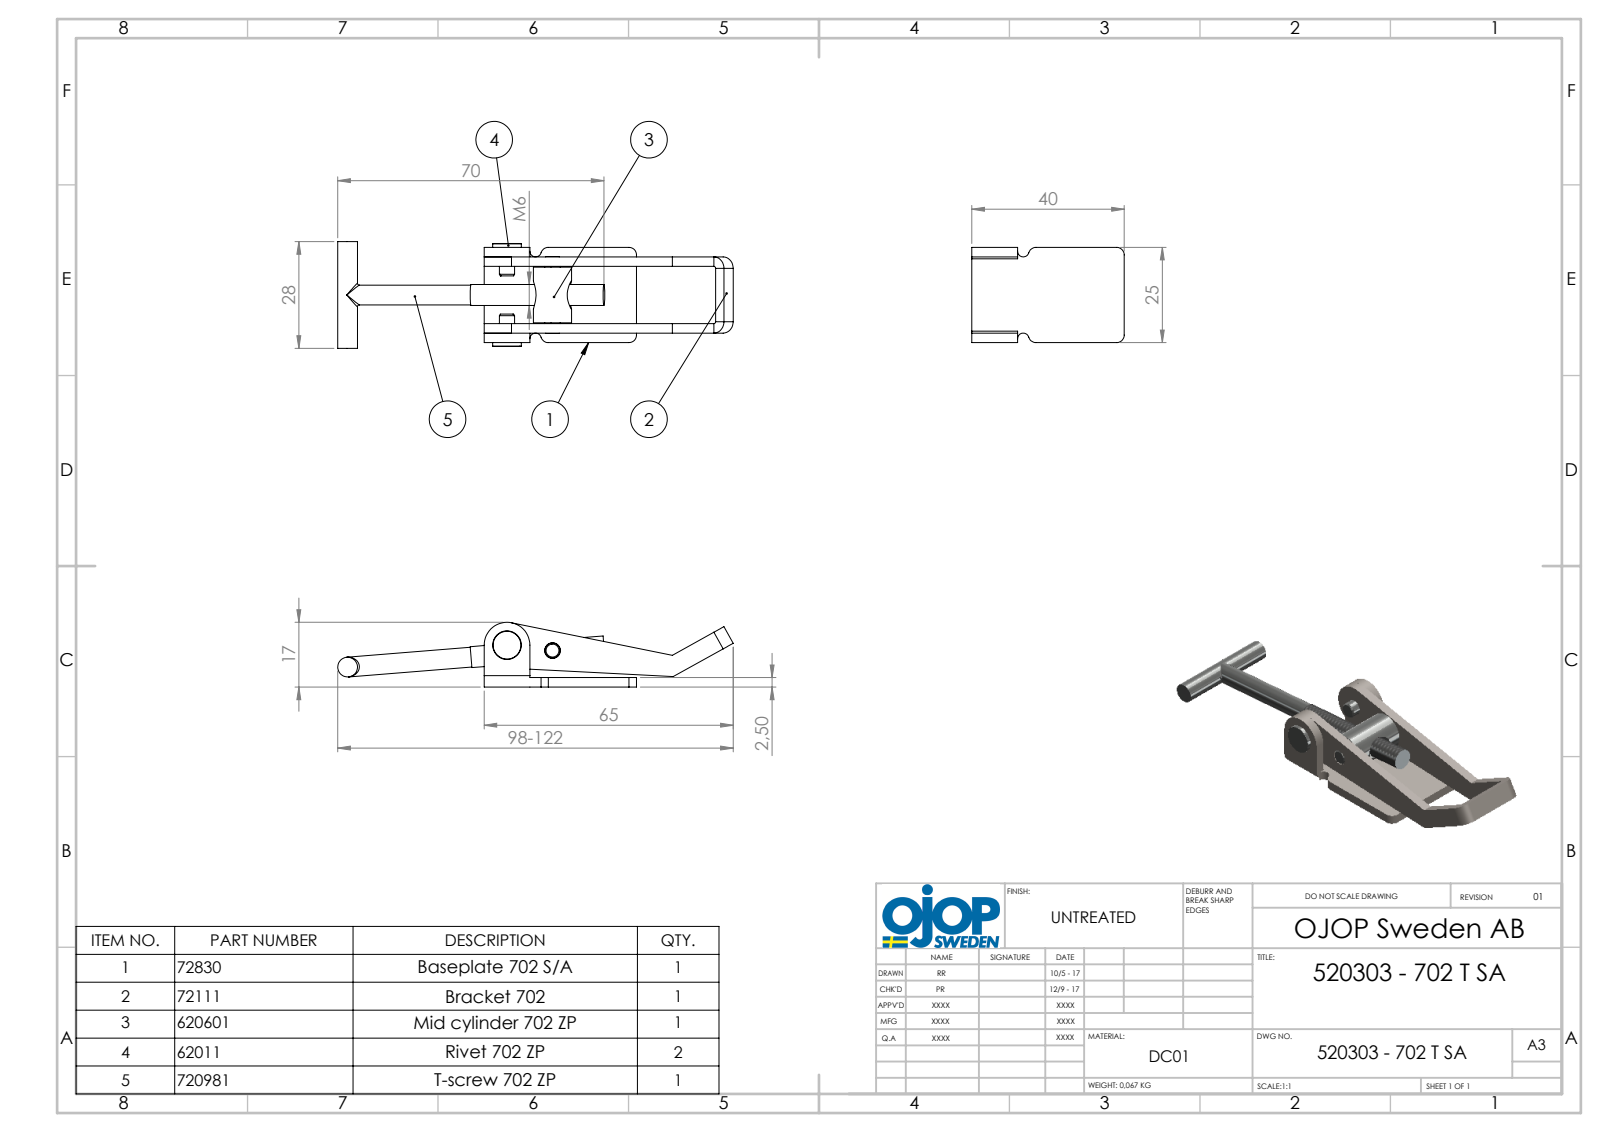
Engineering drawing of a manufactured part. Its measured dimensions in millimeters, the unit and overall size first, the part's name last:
Units: millimetres
Overall size (bounding box): 104.82 × 28 × 17
Round holes (diameter × count): ⌀4.1 ×2, ⌀5 ×1, ⌀6 ×1
Round bosses / shafts (diameter × count): ⌀5.28 ×2, ⌀4 ×2, ⌀10 ×1, ⌀7.5 ×1, ⌀6 ×1
Partial cylindrical surfaces — rounded edges, fillets, slot ends (radius × count): R0.5 ×4, R2 ×4, R3 ×4, R1.5 ×2, R6 ×1
Main face-to-face distances: 2.5, 20, 17.5, 15, 5, 22.5, 25, 19.8, 5.2, 2.7
Hole centre spacings: 12.03
Volume: 9 315 mm³ · Surface area: 8 894 mm²
Bodies: 6 solids, 132 faces (56 planar, 58 cylindrical, 18 other)
Part name (STEP PRODUCT): 702 - Platta SA; 702 - Bygel; 702 - Rulle; 702 - Ansatsnit (+2 more)
STEP written by: SolidWorks 2015 (AUTOMOTIVE_DESIGN)
